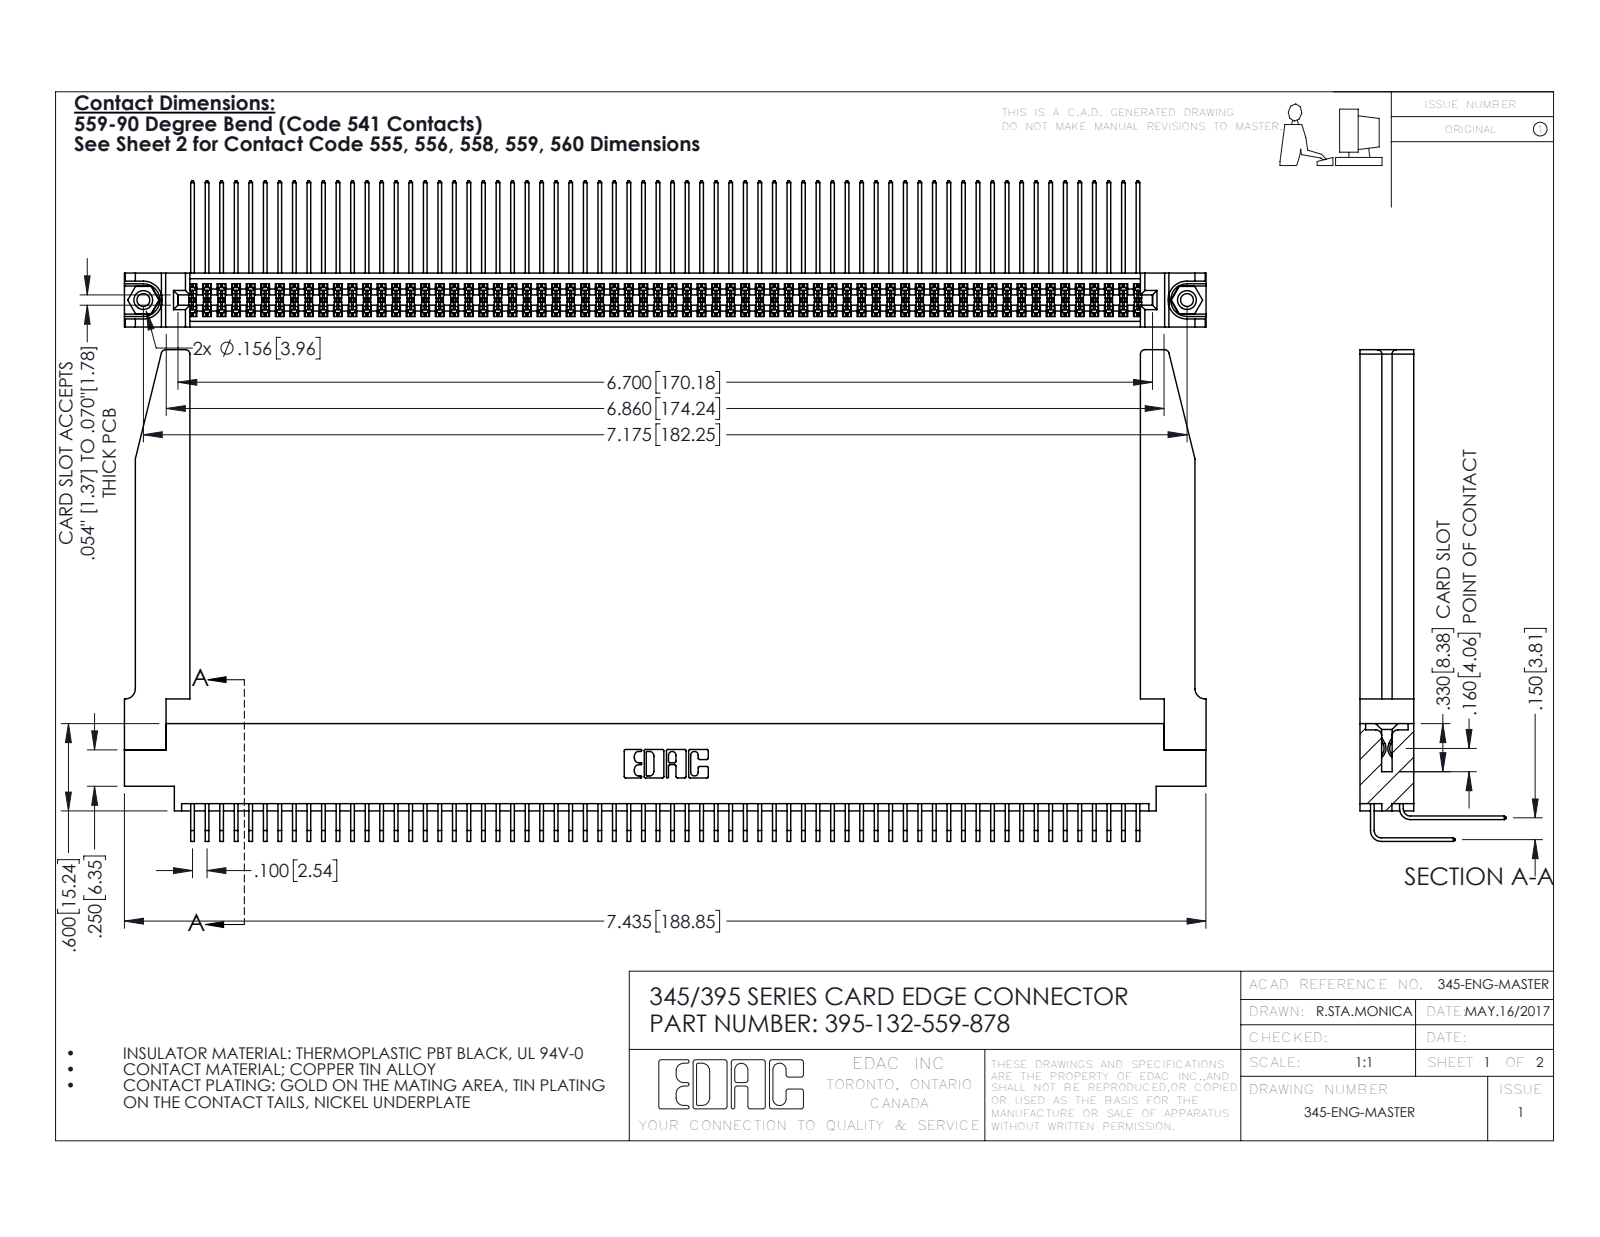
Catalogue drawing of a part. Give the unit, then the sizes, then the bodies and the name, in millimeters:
Units: millimetres
Overall size (bounding box): 188.9 × 85.8 × 25.5
Round holes (diameter × count): ⌀2.3 ×2, ⌀3.2 ×2, ⌀4 ×2, ⌀1.6 ×1
Round bosses / shafts (diameter × count): ⌀3.9 ×2
Partial cylindrical surfaces — rounded edges, fillets, slot ends (radius × count): R0.2 ×198, R0.3 ×22, R0.8 ×8, R0.2 ×6, R0.8 ×6, R0.7 ×3, R0.4 ×2, R0.5 ×2
Main face-to-face distances: 1.8, 7.6, 9.4, 2.5, 6.9, 0.6, 5.1, 5.7, 3.8, 4.4
Hole centre spacings: 6.9, 176.3, 182.2
Volume: 26 990 mm³ · Surface area: 39 430 mm²
Bodies: 137 solids, 7228 faces (4846 planar, 2330 cylindrical, 52 other)
Part name (STEP PRODUCT): 345 Part_0.170 Offset - 0.156 Dia-TH; 345-292-001_559 Tail - 2; 345-250-001_345-250-001-102; 395-132-559-878 (+2 more)
STEP written by: SolidWorks 2016 (CONFIG_CONTROL_DESIGN)
